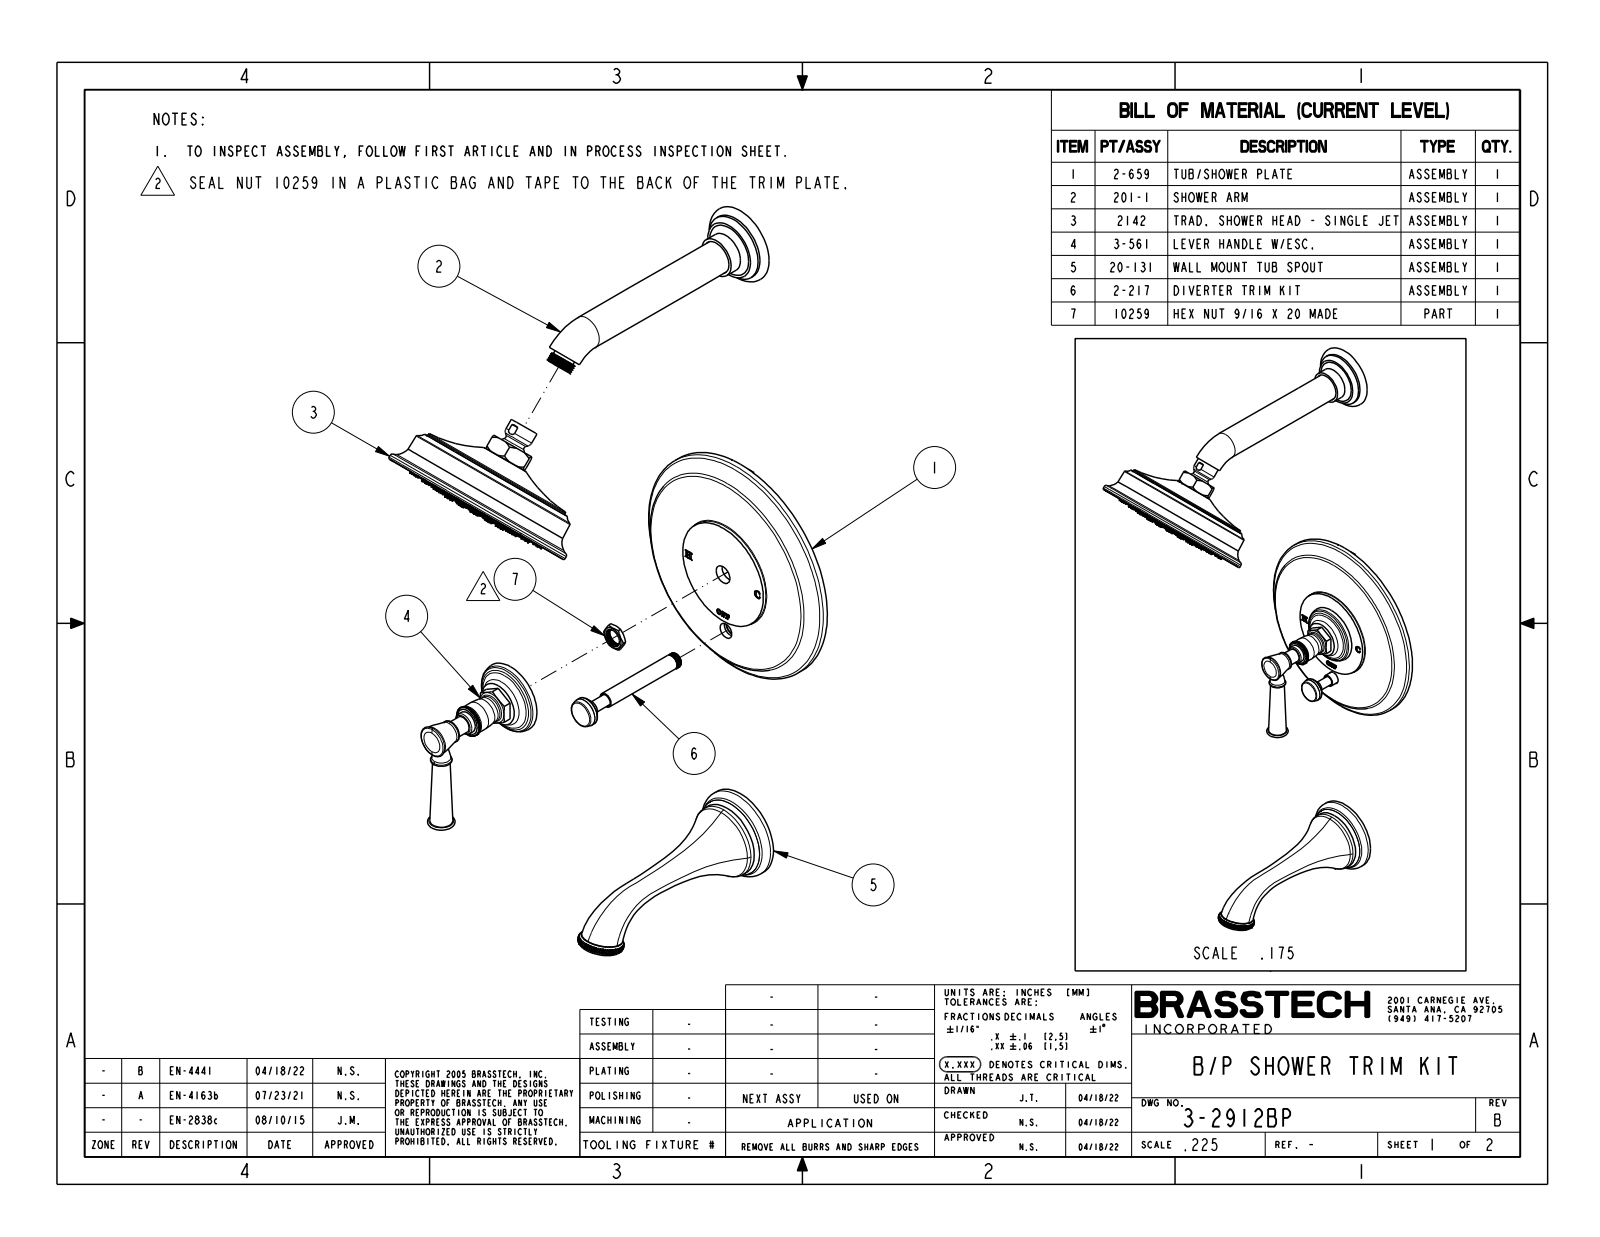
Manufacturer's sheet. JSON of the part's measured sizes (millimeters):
{"part_name": "3-2912BP", "step_written_by": "CREO PARAMETRIC BY PTC INC, 2018400 (CONFIG_CONTROL_DESIGN)", "units": "millimeters", "bodies": {"solids": 3, "faces": 1664, "planar": 587, "cylindrical": 228, "other": 849}, "overall_size": [626.8, 304.7, 190.5], "volume_mm3": 1380000, "surface_area_mm2": 182300, "round_holes": [[1.3, 90], [5.6, 1], [15.3, 1], [134, 1]], "round_bosses_or_shafts": [[190.5, 1], [157.5, 1], [132.6, 1], [122.7, 1], [72.4, 1], [63.7, 1], [59.6, 1], [53.6, 1]], "face_to_face_distances": [15.9, 3.2, 19.1, 0.4, 18.7, 15.5, 25.8, 32.6, 32.2, 16.7], "hole_center_spacings": [12.2, 46.7, 24.2, 46.7, 35.8, 57.7, 57.7, 12]}
